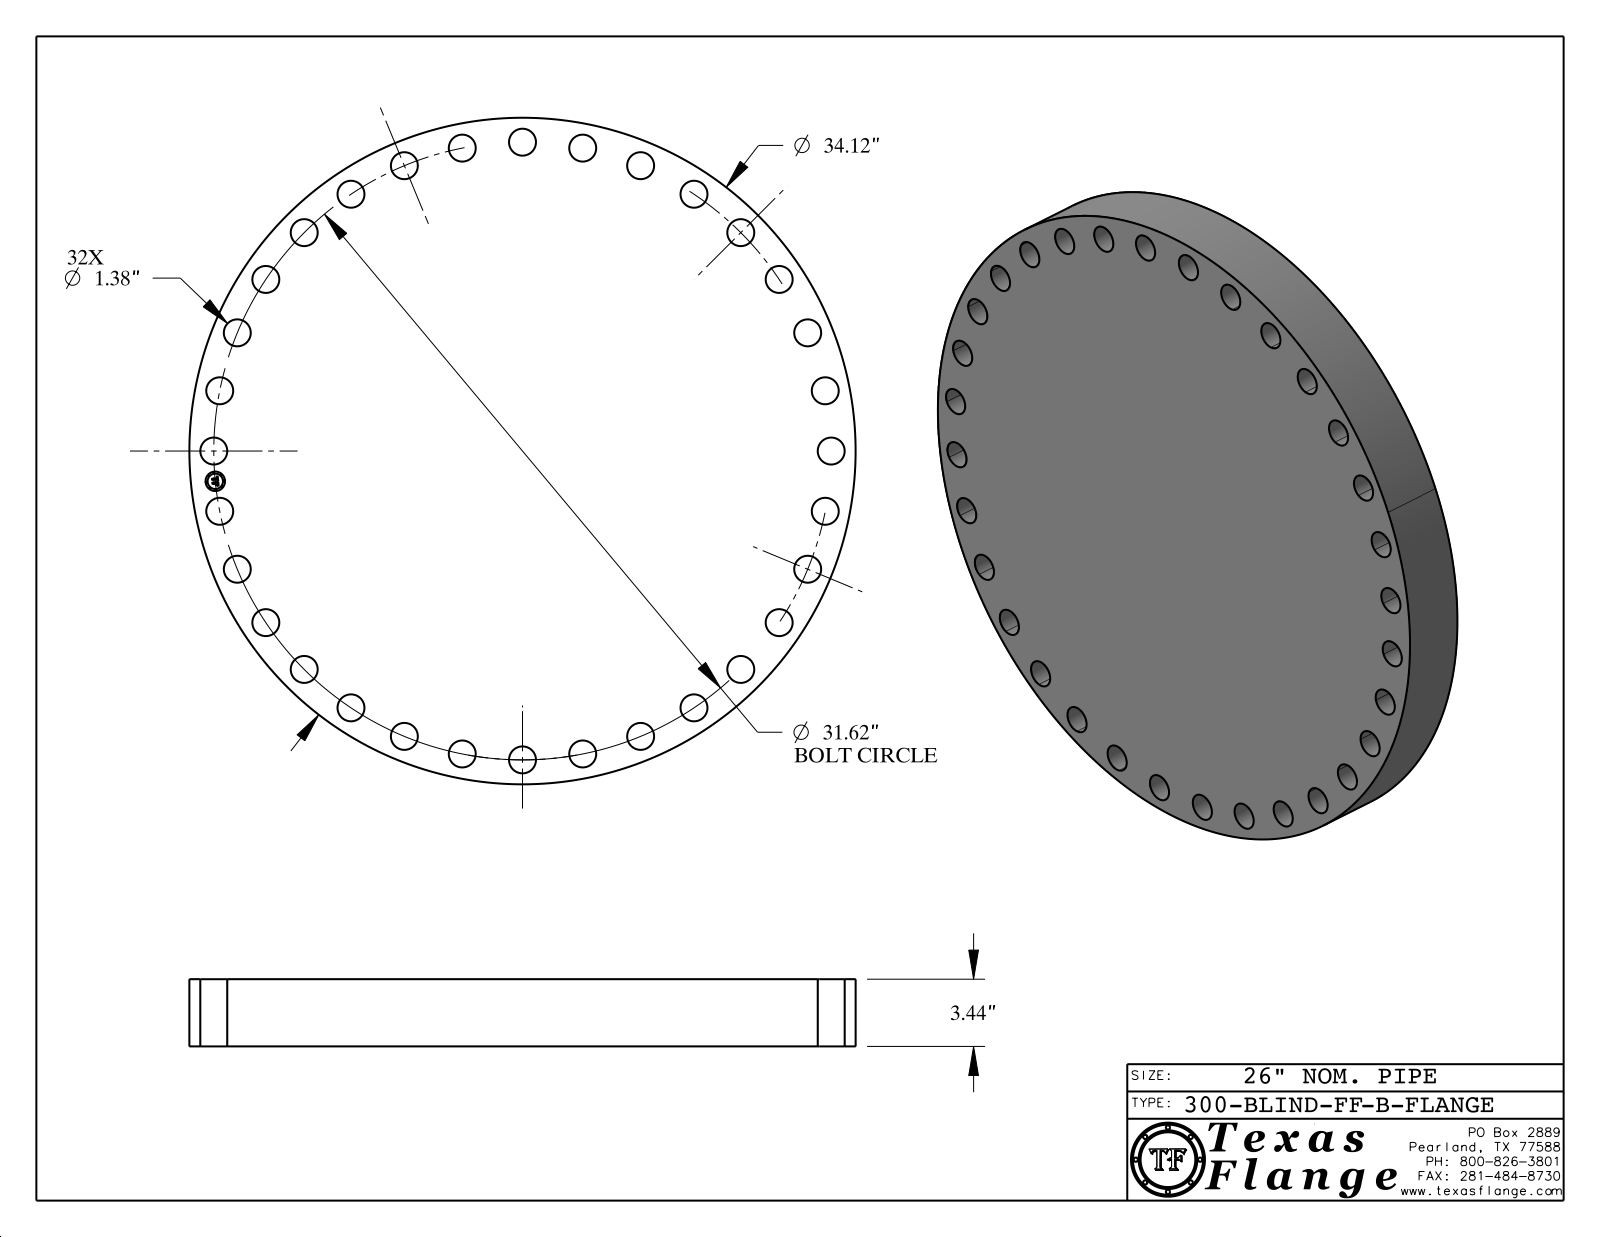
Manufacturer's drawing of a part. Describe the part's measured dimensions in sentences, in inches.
The part is named "300-BLIND-FF, Series B". Its 3-D file was written by "CATIA V5 STEP AP214 (AUTOMOTIVE_DESIGN)". It is 1 solid with 453 faces: 367 planar, 86 cylindrical and 0 other. Overall it measures 34.12 by 34.12 by 3.44 inches. Its volume is 2 981 cubic inches and its surface area 2 579 square inches. Round holes: 32 of diameter 1.38, 1 of diameter 1. Round bosses or shafts: 8 of diameter 0.061, 1 of diameter 34.12, 1 of diameter 0.788. The main face-to-face distances are 3.44, 3.425, 0.015, 0.298, 0.293, 0.054, 0.193, 0.248, 0.044, 0.15. The hole center spacings are 6.169, 26.291, 31.468, 27.887, 30.259, 14.906, 20.059, 31.013.
